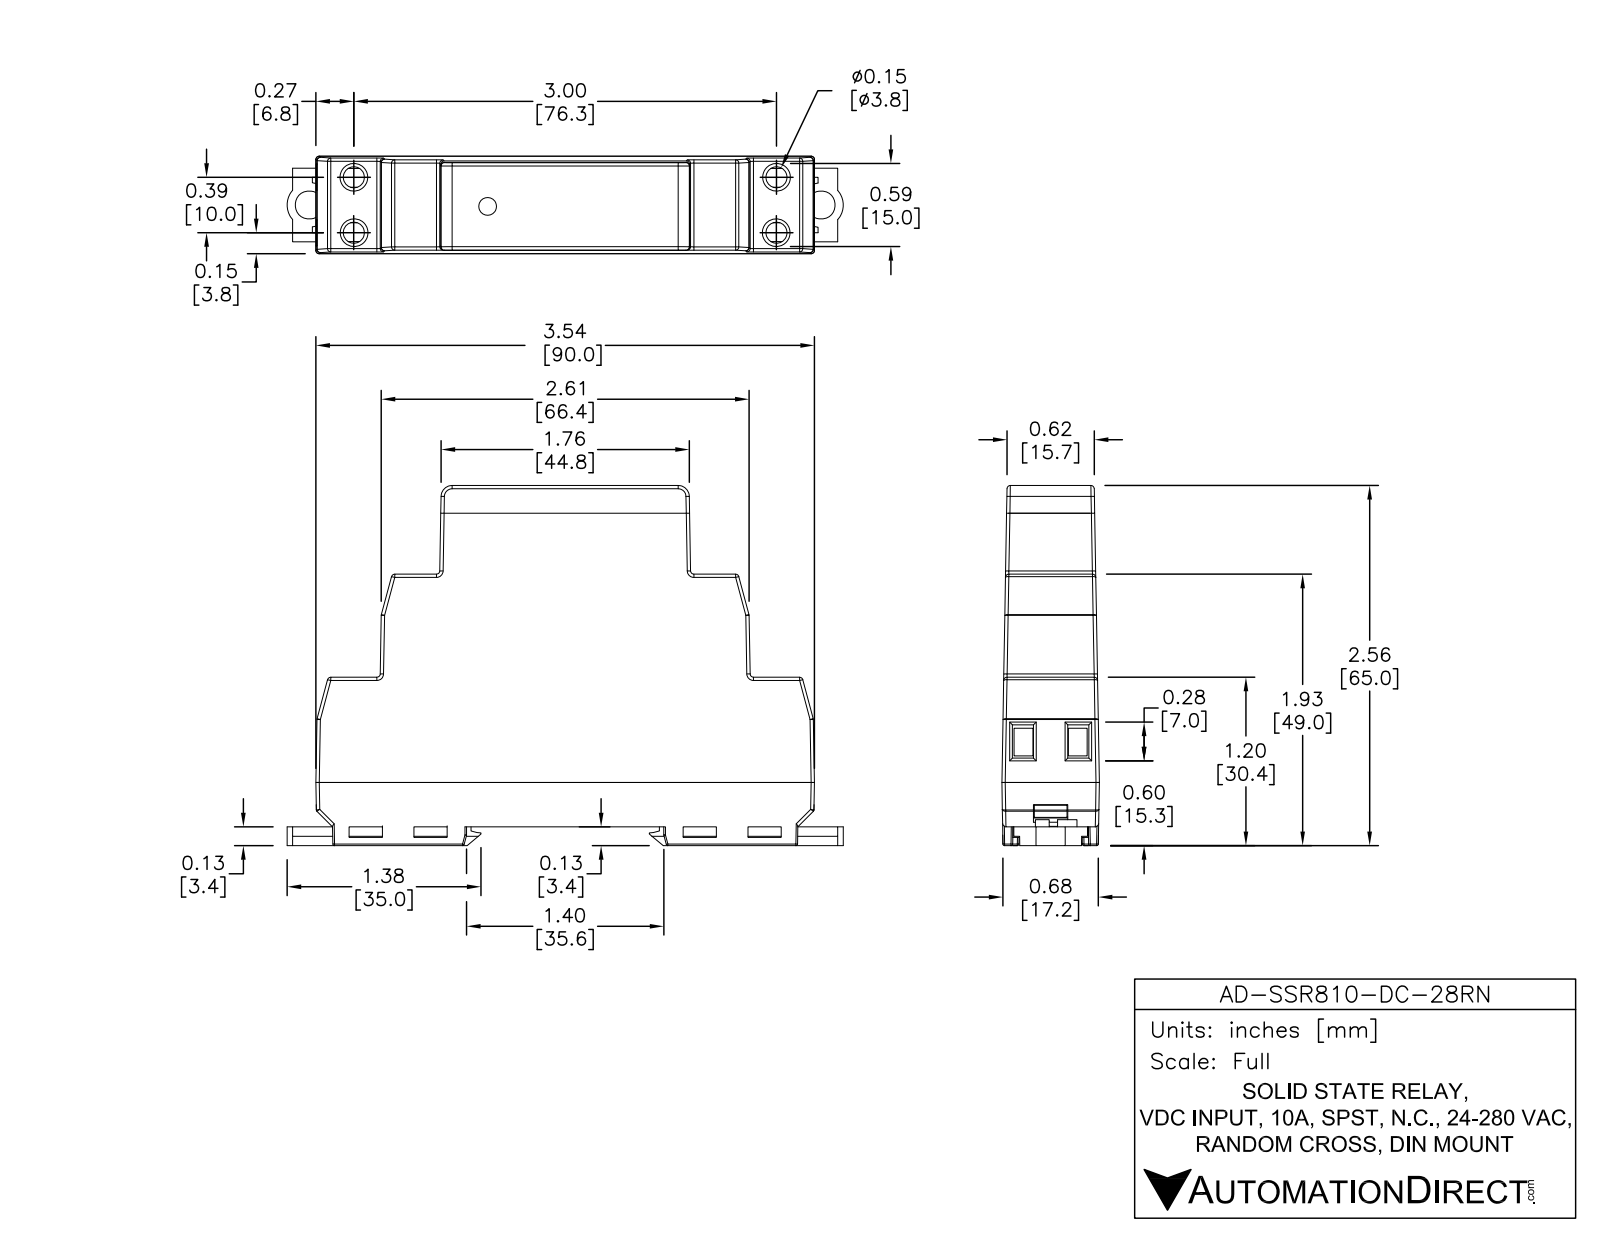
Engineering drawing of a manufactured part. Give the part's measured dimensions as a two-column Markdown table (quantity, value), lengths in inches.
| quantity | value |
| --- | --- |
| part name | AD-SSR810-DC-28RN |
| STEP written by | SolidWorks 2013 (AUTOMOTIVE_DESIGN) |
| units | inches |
| bodies | 1 solid, 855 faces (501 planar, 78 cylindrical, 276 other) |
| overall size | 3.924 × 2.616 × 0.685 |
| volume | 4.605 in³ |
| surface area | 24.23 in² |
| round holes (diameter × count) | 0.19 × 4, 0.2 × 2 |
| round bosses / shafts (diameter × count) | 0.105 × 1 |
| partial cylindrical surfaces (radius × count) | 0.015 × 41, 0.06 × 2, 0.172 × 2 |
| main face-to-face distances | 2.525, 0.049, 2.574, 0.425, 2.215, 0.025, 0.05, 1.934, 1.885, 0.64 |
| hole center spacings | 0.338, 3.3, 0.364, 3.01, 3.032, 3.58 |
